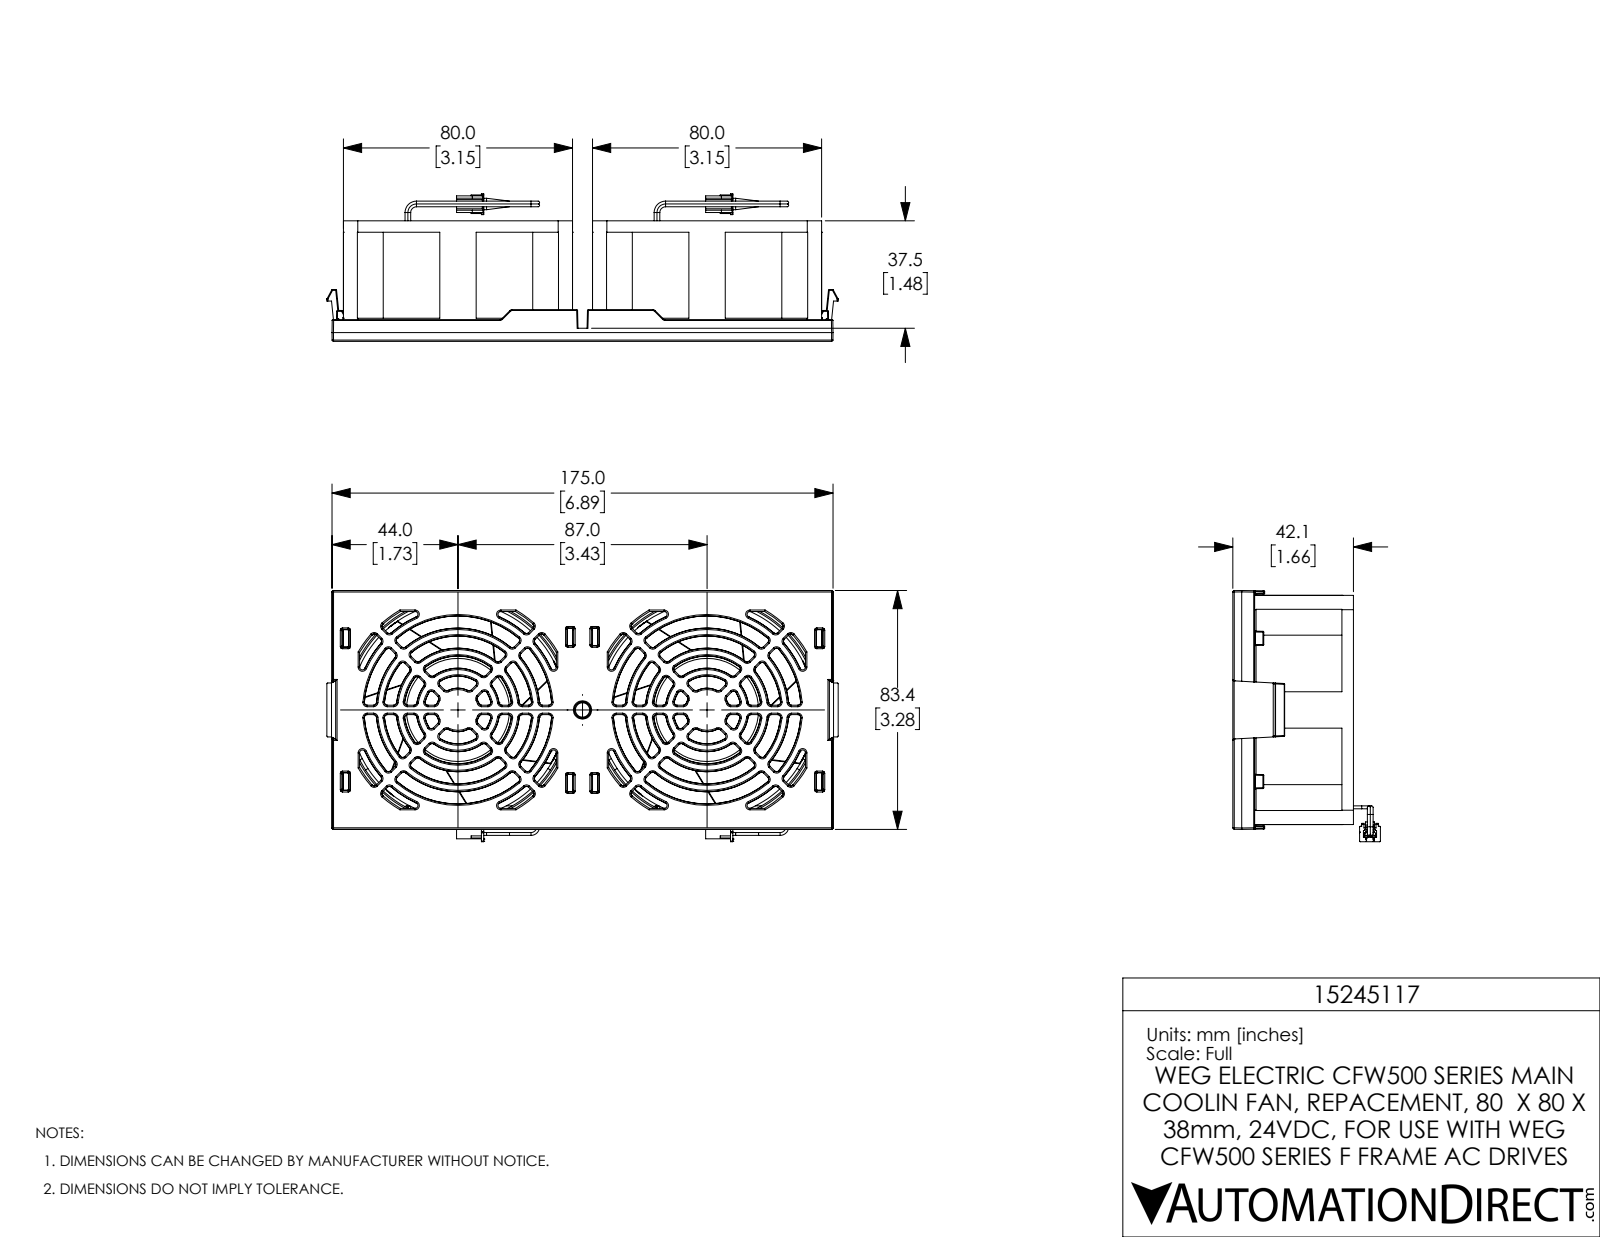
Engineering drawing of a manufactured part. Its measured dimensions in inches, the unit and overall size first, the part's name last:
Units: inches
Overall size (bounding box): 7.029 × 3.453 × 2.03
Round holes (diameter × count): ⌀0.169 ×8, ⌀3.031 ×2
Round bosses / shafts (diameter × count): ⌀0.039 ×14, ⌀2.953 ×2, ⌀1.575 ×2
Partial cylindrical surfaces — rounded edges, fillets, slot ends (radius × count): R0.012 ×270, R0.02 ×48, R0.004 ×16, R0.197 ×8, R0.01 ×4, R0.039 ×4, R1.594 ×2
Main face-to-face distances: 0.122, 1.657, 1.535, 1.496, 0.039, 0.161, 3.15, 0.157, 1.052, 1.894
Hole centre spacings: 1.991, 2.815, 3.425, 2.46, 3.981, 4.433, 5.033, 0.61
Volume: 12.92 in³ · Surface area: 214.2 in²
Bodies: 9 solids, 3070 faces (1081 planar, 810 cylindrical, 1179 other)
Part name (STEP PRODUCT): 10006241061swa000 NC
STEP written by: SolidWorks 2017 (AUTOMOTIVE_DESIGN)
